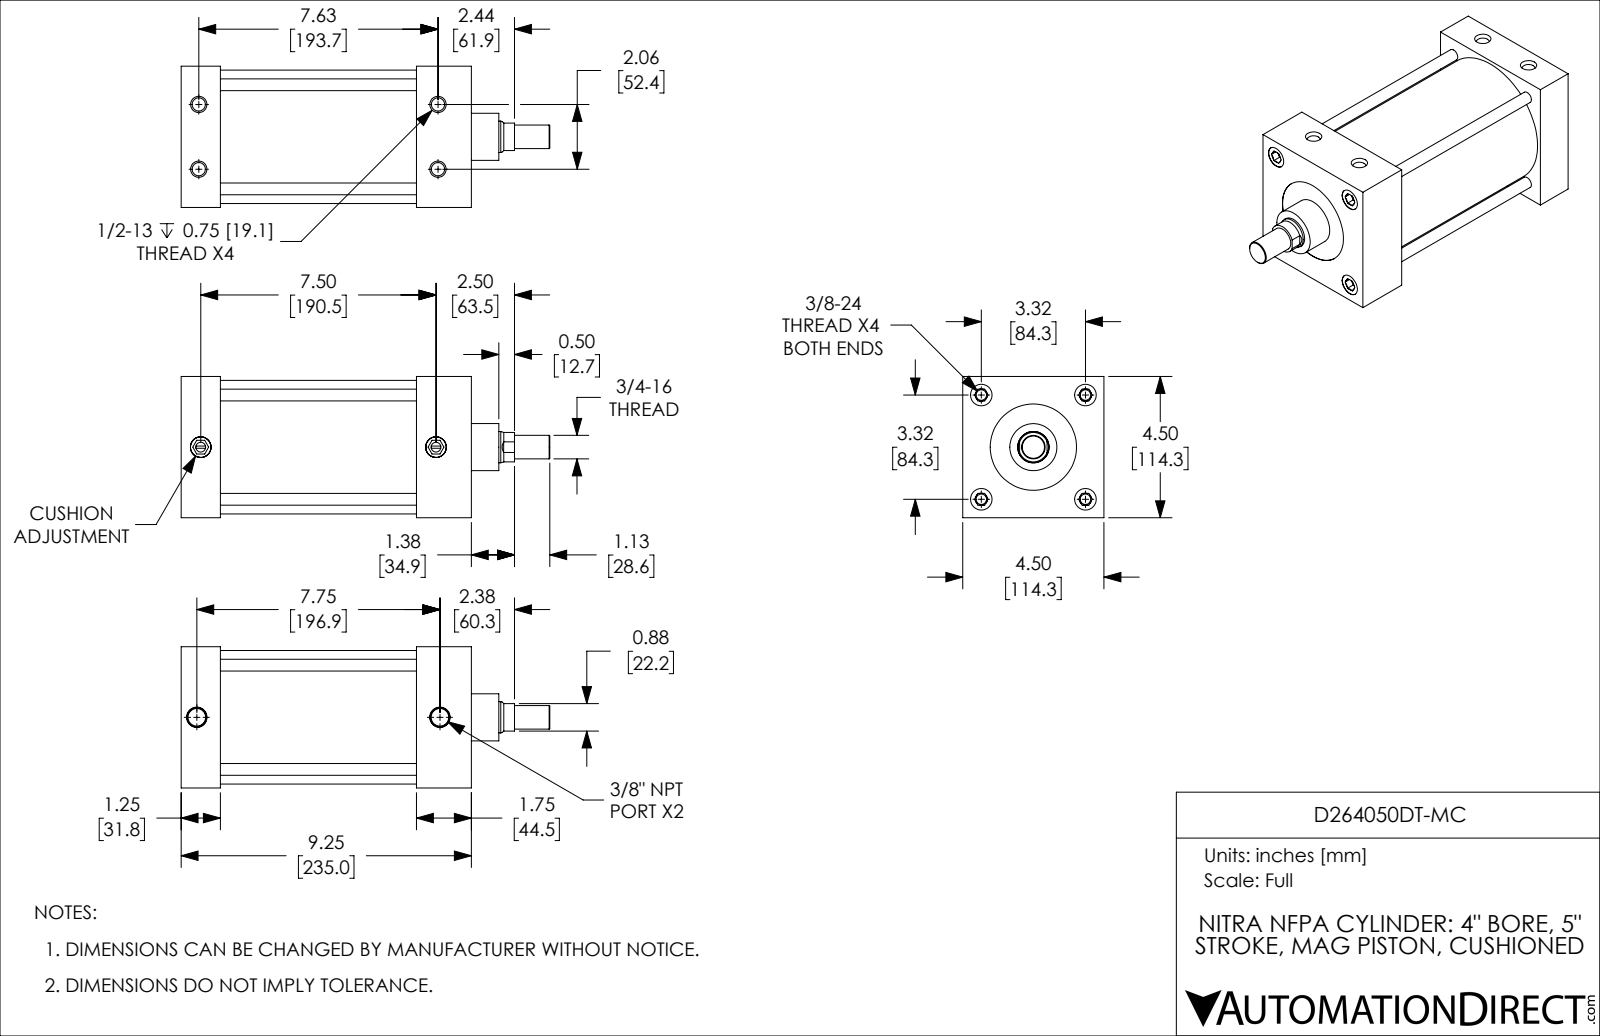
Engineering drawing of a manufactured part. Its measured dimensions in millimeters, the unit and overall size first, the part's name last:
Units: millimetres
Overall size (bounding box): 298.5 × 114.3 × 114.3
Round holes (diameter × count): ⌀8.4 ×4, ⌀10.7 ×4, ⌀17.4 ×4, ⌀7.9 ×2, ⌀14.3 ×2, ⌀16.7 ×2, ⌀25.4 ×1, ⌀69.9 ×1, ⌀101.6 ×1
Round bosses / shafts (diameter × count): ⌀9.5 ×4, ⌀16.7 ×2, ⌀108 ×1, ⌀101.6 ×1, ⌀38.1 ×1, ⌀25.4 ×1, ⌀19.1 ×1
Partial cylindrical surfaces — rounded edges, fillets, slot ends (radius × count): R11.9 ×1
Main face-to-face distances: 31.8, 114.3, 190.5, 158.8, 235, 203.2, 44.5, 63.5, 127, 171.5
Hole centre spacings: 26.2, 59.6, 84.3, 197, 52.4, 119.3, 193.7, 200.6
Volume: 1 527 000 mm³ · Surface area: 274 600 mm²
Bodies: 4 solids, 246 faces (90 planar, 78 cylindrical, 78 other)
Part name (STEP PRODUCT): D264050DT-MC_PISTON_KK1; D264050DT-MC; D264050DT-MC_BODY; D264050DT-MC_CUSHION
STEP written by: SolidWorks 2019 (CONFIG_CONTROL_DESIGN)
